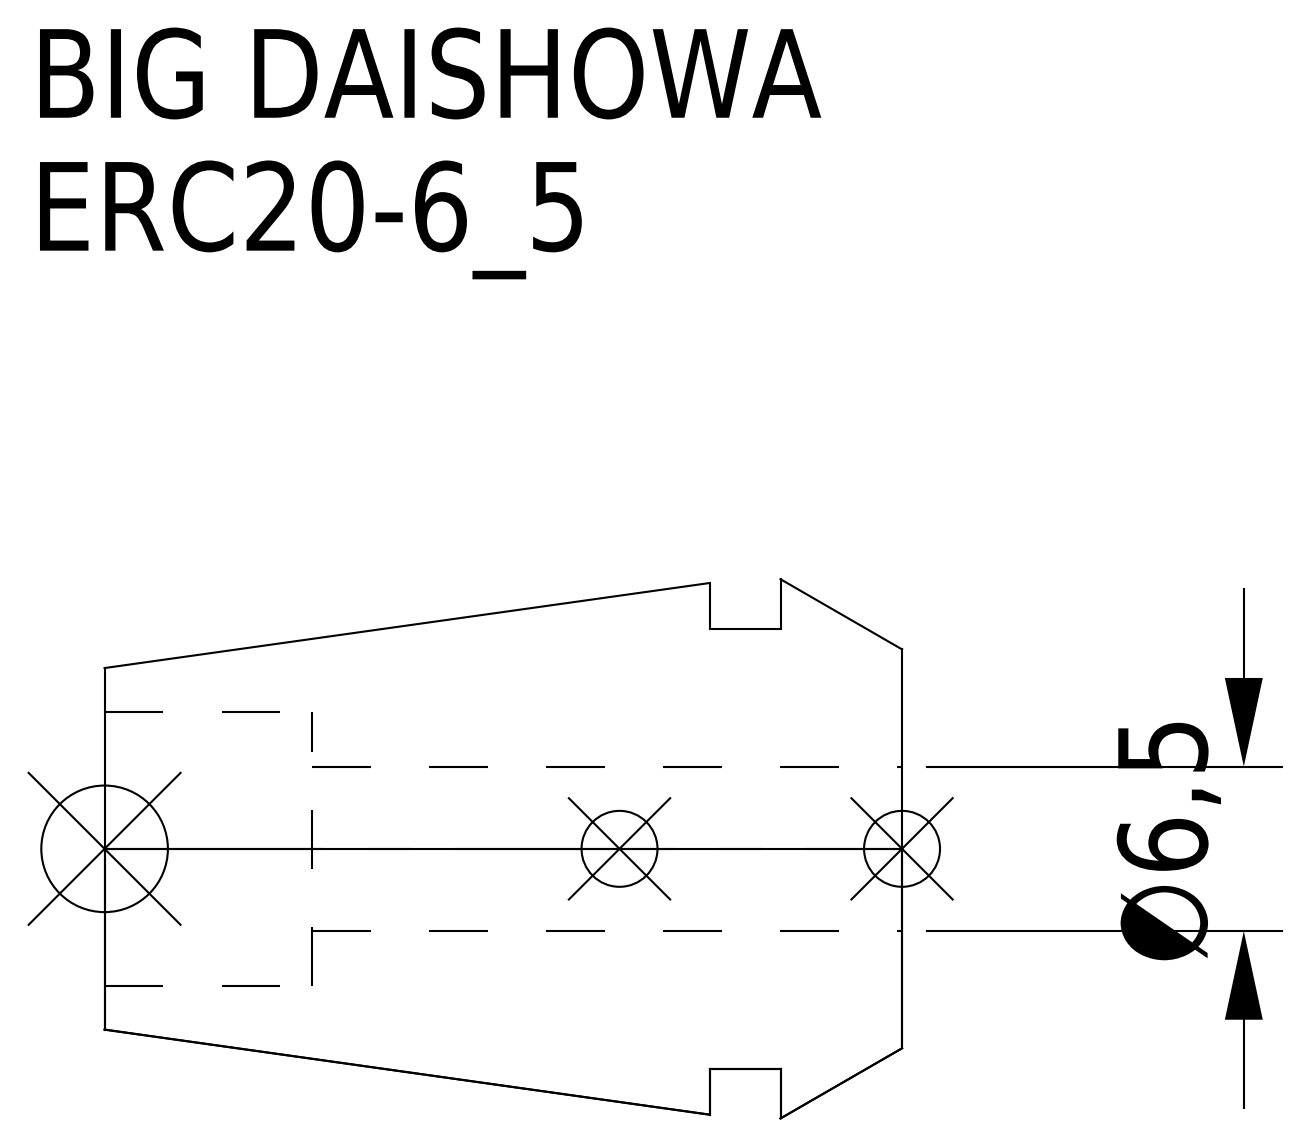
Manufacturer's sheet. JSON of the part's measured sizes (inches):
{"part_name": "ERC20-6_5", "step_written_by": "CREO PARAMETRIC BY PTC INC, 2016380 (AUTOMOTIVE_DESIGN)", "units": "inches", "bodies": {"solids": 1, "faces": 15, "planar": 5, "cylindrical": 6, "other": 4}, "overall_size": [1.24, 0.839, 0.839], "volume_in3": 0.388, "surface_area_in2": 4.779, "round_holes": [[0.256, 1], [0.425, 1]], "round_bosses_or_shafts": [[0.685, 1]], "face_to_face_distances": [0.189, 0.299, 0.11, 1.24, 1.051, 0.941, 0.917, 0.728, 0.618, 0.323]}
